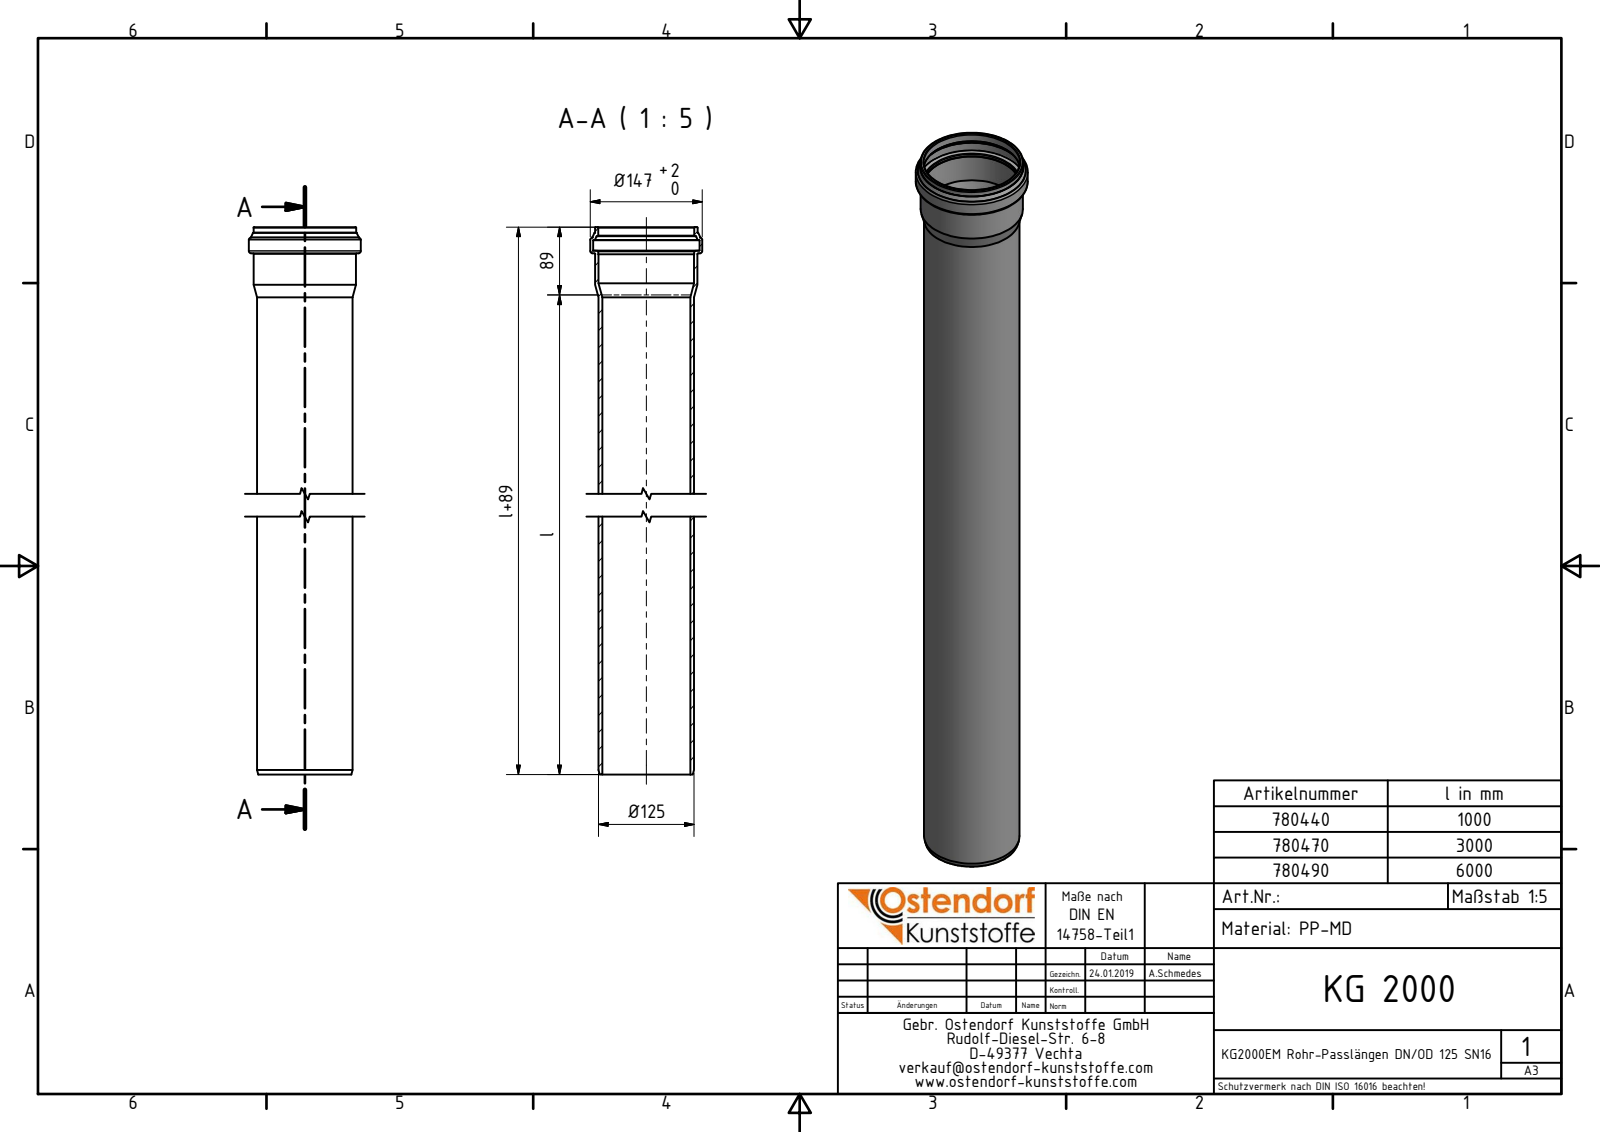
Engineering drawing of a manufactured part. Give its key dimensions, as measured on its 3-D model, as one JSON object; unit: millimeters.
{"part_name": "780440 KG2000EM Rohr-Passlängen DN125x1000 SN16", "step_written_by": "Autodesk Inventor 2016 (AUTOMOTIVE_DESIGN)", "units": "millimeters", "bodies": {"solids": 1, "faces": 37, "planar": 6, "cylindrical": 9, "other": 22}, "overall_size": [1089, 147, 147], "volume_mm3": 2027000, "surface_area_mm2": 842215, "round_holes": [[115.6, 1], [125.5, 1], [126, 1], [139.8, 1]], "round_bosses_or_shafts": [[147, 1], [134.8, 1], [134.3, 1], [125.4, 1]], "face_to_face_distances": [1054.7, 1089, 34.3, 1075.4, 20.7, 13.6, 1053.48, 1.22, 21.92, 35.52]}
